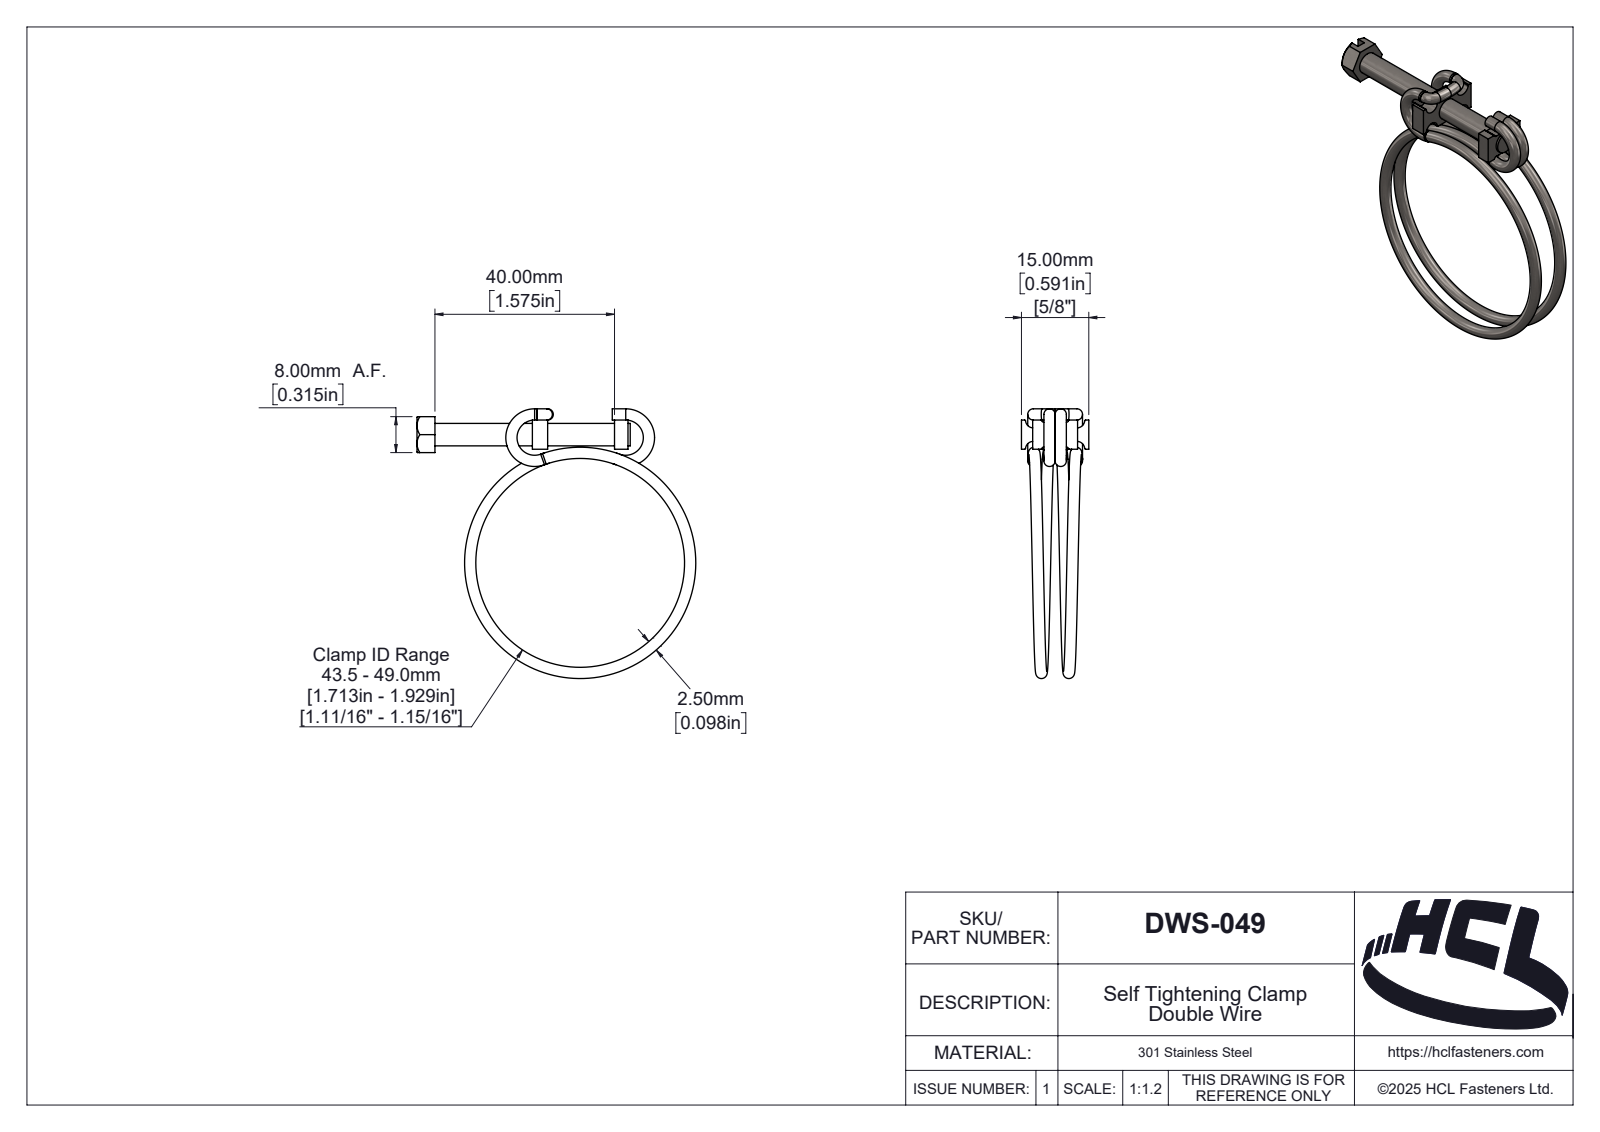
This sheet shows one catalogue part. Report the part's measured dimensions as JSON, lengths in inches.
{"part_name": "DWS-049", "step_written_by": "SolidWorks 2025 (AUTOMOTIVE_DESIGN)", "units": "inches", "bodies": {"solids": 6, "faces": 213, "planar": 55, "cylindrical": 74, "other": 84}, "overall_size": [2.445, 2.364, 0.591], "volume_in3": 0.213, "surface_area_in2": 7.64, "round_holes": [[0.197, 1]], "round_bosses_or_shafts": [[0.098, 4]], "partial_cylinders_radius": [[0.008, 12], [0.02, 4], [0.069, 4], [0.016, 1], [0.02, 1], [0.021, 1], [0.025, 1], [0.036, 1]], "face_to_face_distances": [0.157, 0.256, 0.236, 0.02, 0.134, 0.079, 0.72, 0.587, 0.839, 0.705]}
